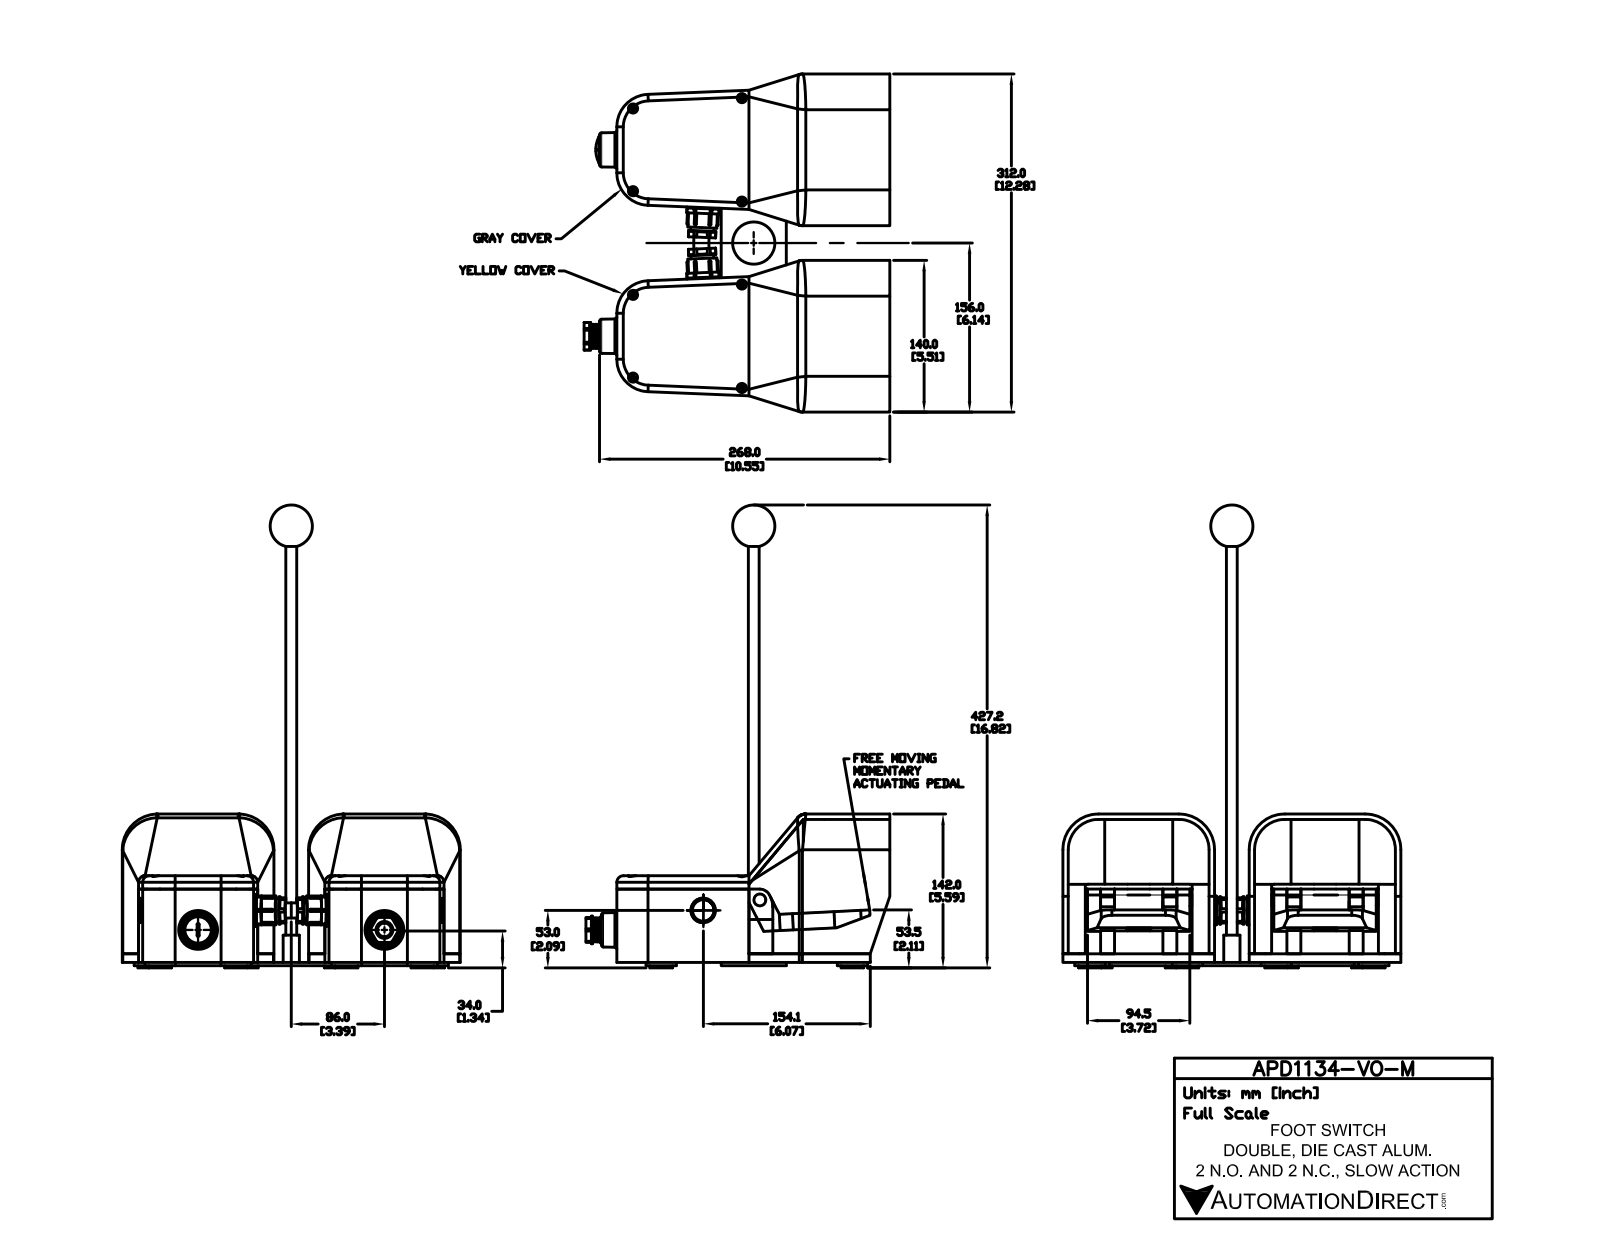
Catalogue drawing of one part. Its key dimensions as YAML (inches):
part_name: "APD1134-V0-M"
step_written_by: "SolidWorks 2015 (AUTOMOTIVE_DESIGN)"
units: inches
bodies: {solids: 36, faces: 829, planar: 502, cylindrical: 213, other: 114}
overall_size: [16.817, 12.283, 11.112]
volume: 196.2
surface_area: 892.6
round_holes:
  - {diameter: 0.335, count: 8}
  - {diameter: 0.896, count: 4}
  - {diameter: 0.498, count: 1}
  - {diameter: 0.614, count: 1}
round_bosses_or_shafts:
  - {diameter: 1.102, count: 8}
  - {diameter: 0.827, count: 8}
  - {diameter: 0.782, count: 4}
  - {diameter: 1.171, count: 2}
  - {diameter: 1.051, count: 2}
  - {diameter: 0.992, count: 2}
  - {diameter: 0.846, count: 2}
  - {diameter: 1.004, count: 1}
partial_cylinders:
  - {radius: 0.039, count: 34}
  - {radius: 0.042, count: 12}
  - {radius: 0.394, count: 10}
  - {radius: 0.236, count: 5}
  - {radius: 1.102, count: 4}
  - {radius: 1.181, count: 4}
  - {radius: 1.299, count: 4}
  - {radius: 0.787, count: 1}
face_to_face_distances: [0.197, 5.315, 6.772, 0.315, 2.348, 5.512, 2.664, 2.349, 2.663, 0.118]
hole_center_spacings: [3.976, 5.206, 6.772, 3.004, 3.76, 5.211, 7.52, 8.172]
